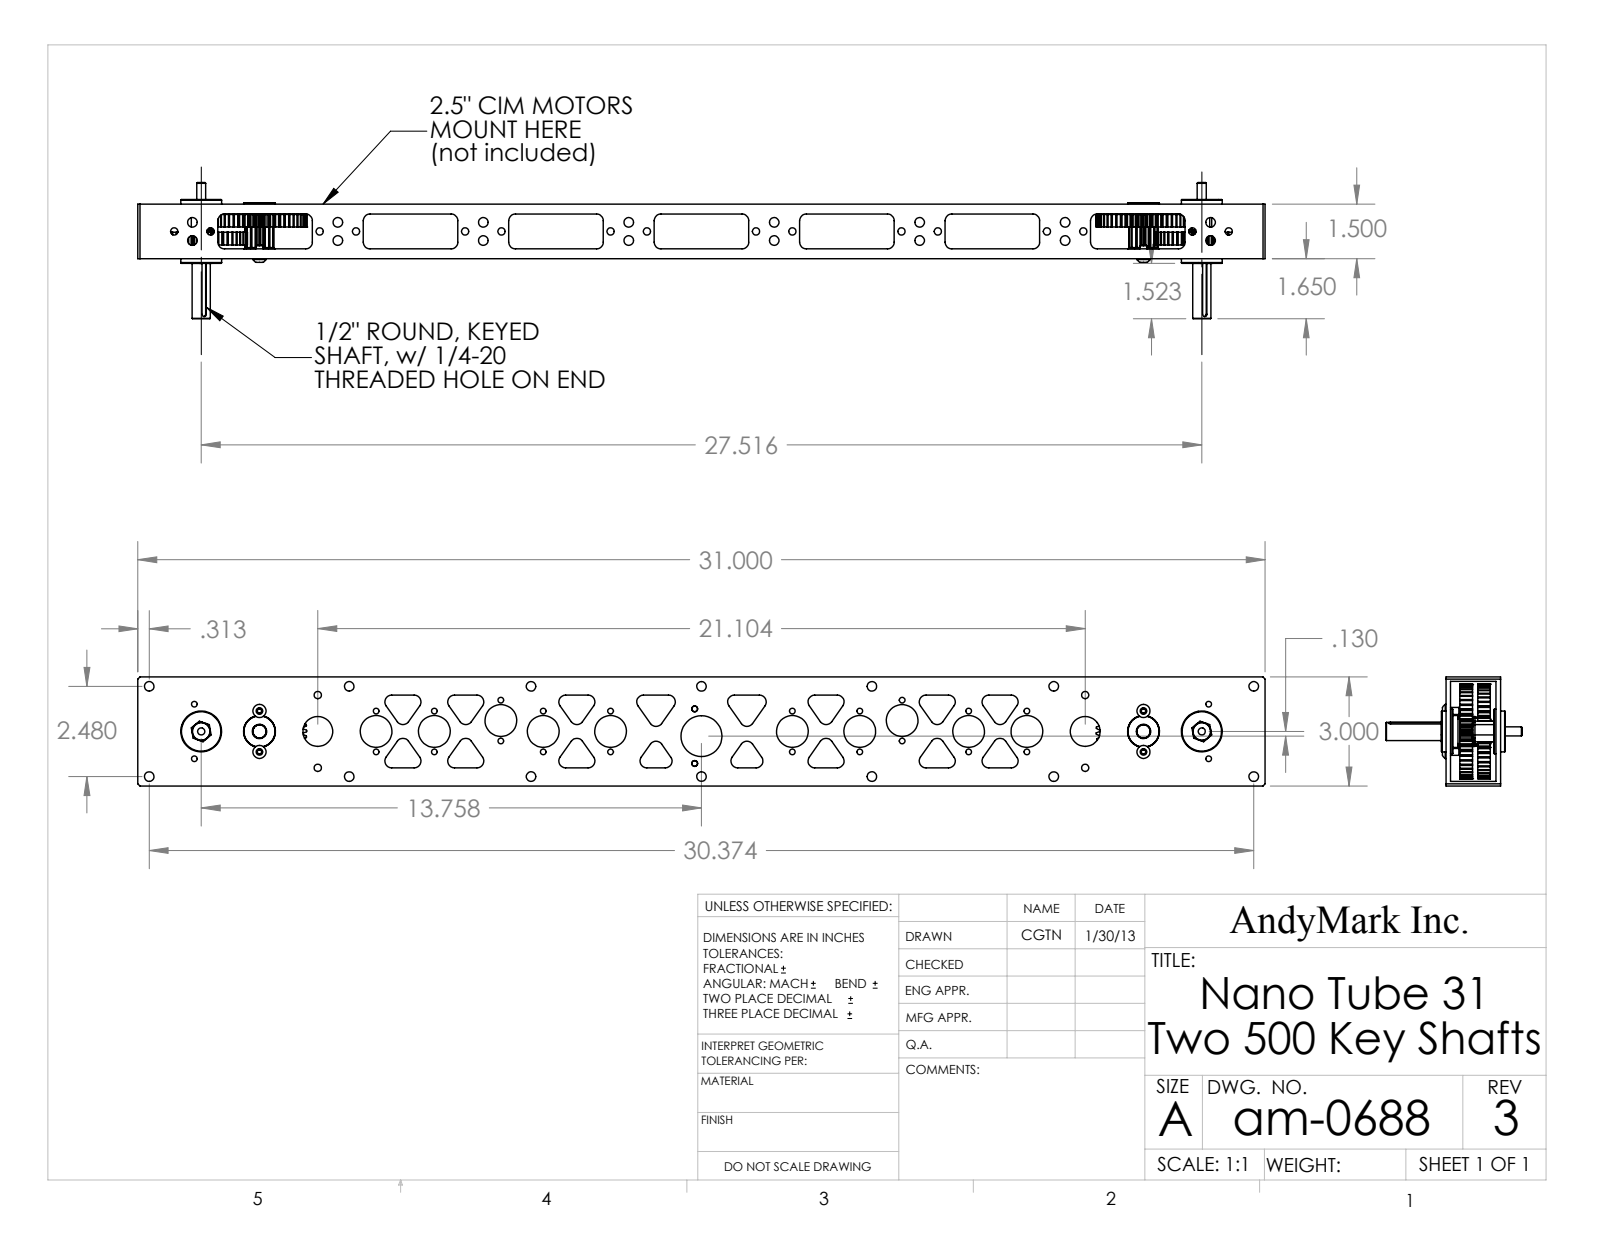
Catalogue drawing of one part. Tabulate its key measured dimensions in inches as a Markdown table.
| quantity | value |
| --- | --- |
| part name | R6ZZ Bearing; fr6; BHCS 10-32 x 0.375 phillips_SBHCSCREW 0.19-32x0.5-HX-C; am-0653 ToughBox Nano Tube 31 Rev3 (+8 more) |
| STEP written by | SolidWorks 2010 (CONFIG_CONTROL_DESIGN) |
| units | inches |
| bodies | 27 solids, 2224 faces (452 planar, 1636 cylindrical, 136 other) |
| overall size | 31 × 3.745 × 3 |
| volume | 33.16 in³ |
| surface area | 532.7 in² |
| round holes (diameter × count) | 0.156 × 30, 0.264 × 30, 0.2 × 16, 0.874 × 12, 0.199 × 4, 1.125 × 3, 0.16 × 2, 0.196 × 2, 0.375 × 2, 0.375 × 2, 0.593 × 2, 0.82 × 2 |
| round bosses / shafts (diameter × count) | 0.875 × 4, 0.361 × 4, 0.19 × 4, 1.225 × 2, 1.125 × 2, 1.1 × 2, 0.972 × 2, 0.499 × 2 |
| partial cylindrical surfaces (radius × count) | 0.6 × 400, 0.187 × 72, 0.34 × 56, 0.02 × 20, 0.008 × 12, 0.06 × 8, 0.04 × 4, 0.064 × 4 |
| main face-to-face distances | 0.125, 0.125, 1.5, 1.375, 1.25, 1.375, 3, 2.875, 2.75, 2.875 |
| hole center spacings | 0.559, 3.509, 4, 4.507, 7.504, 8, 8.504, 11.503 |
